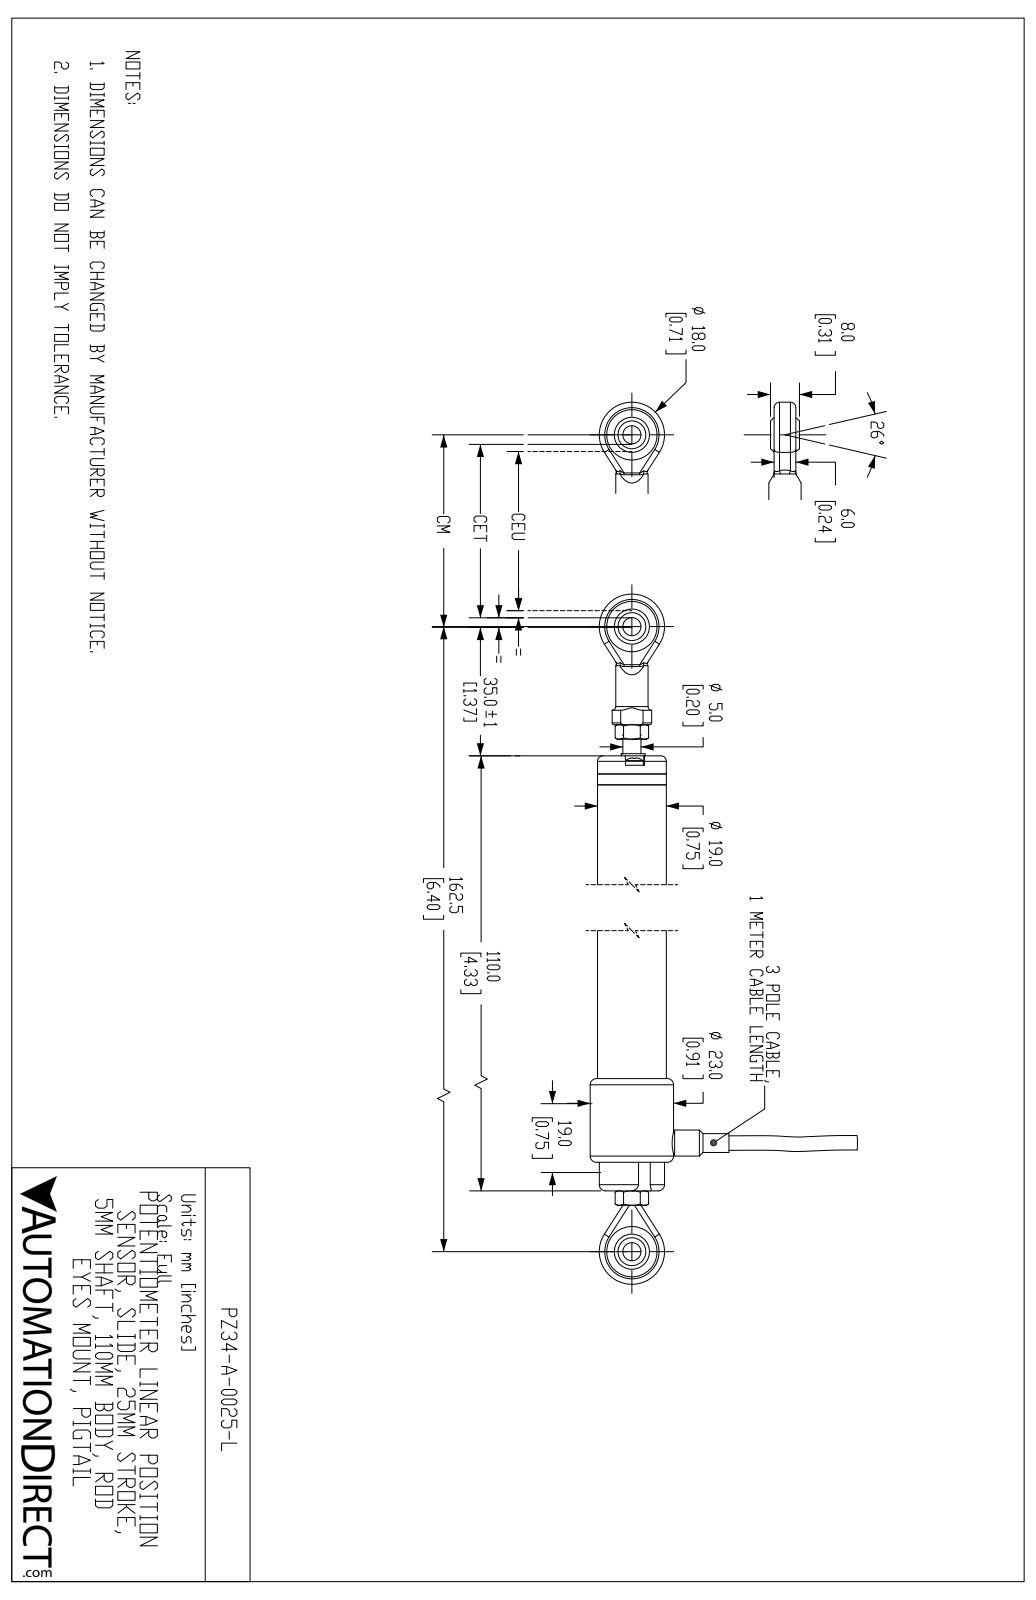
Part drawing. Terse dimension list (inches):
name: PZ34-A-0025-L
written by: SolidWorks 2019 (AUTOMOTIVE_DESIGN)
unit: in
bodies: 18 solids, 688 faces (186 planar, 174 cylindrical, 328 other)
size: 7.106 × 2.904 × 0.906
volume: 2.583 in³; area: 31.47 in²
holes: 4× ⌀0.114, 2× ⌀0.197, 2× ⌀0.209, 2× ⌀0.547, 1× ⌀0.138, 1× ⌀0.165, 1× ⌀0.24, 1× ⌀0.354, 1× ⌀0.75
bosses: 5× ⌀0.197, 4× ⌀0.098, 1× ⌀0.906, 1× ⌀0.748, 1× ⌀0.709, 1× ⌀0.35, 1× ⌀0.283, 1× ⌀0.236
rounds: 8× R0.059, 4× R0.01, 2× R0.02, 2× R0.039, 2× R0.104, 2× R0.354, 1× R0.017, 1× R0.063
face distances: 3.425, 3.307, 0.118, 0.315, 0.224, 0.213, 0.217, 0.051, 0.039, 0.264
hole spacings: 0.269, 0.082, 0.532, 0.539, 6.398
